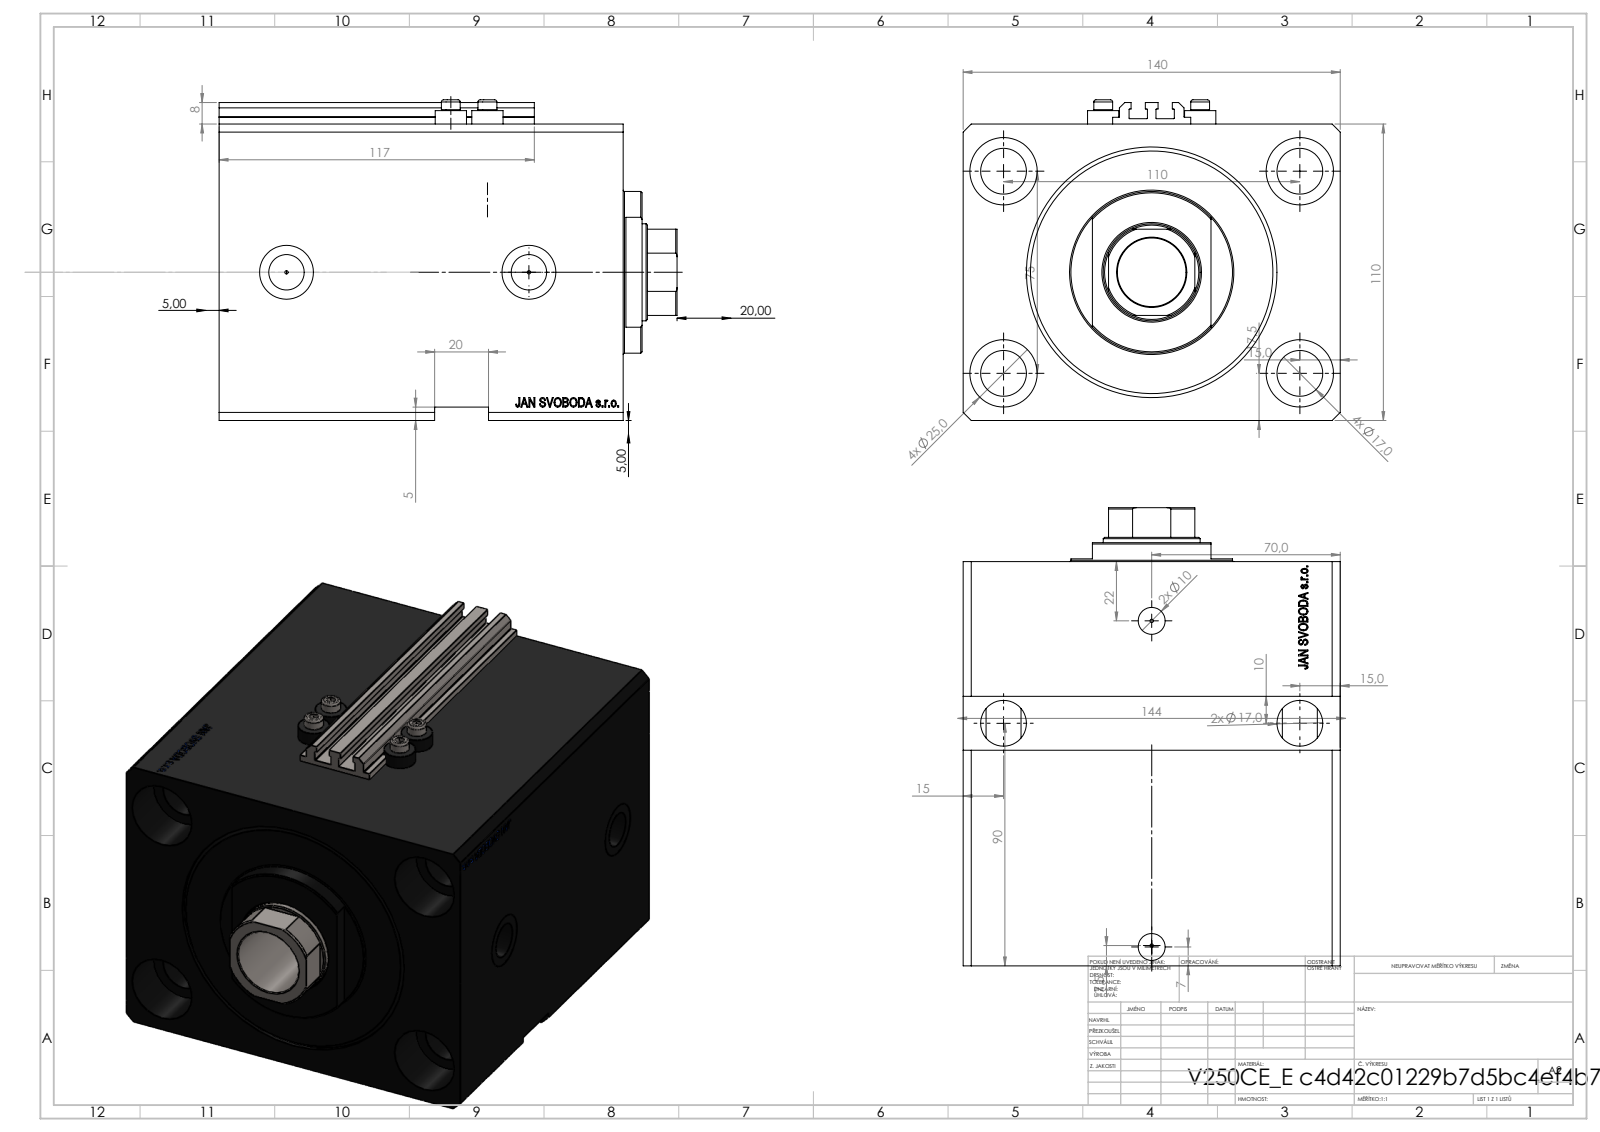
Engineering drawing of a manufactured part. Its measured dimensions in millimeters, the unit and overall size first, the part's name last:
Units: millimetres
Overall size (bounding box): 170 × 140 × 119
Round holes (diameter × count): ⌀17 ×8, ⌀1.25 ×4, ⌀4 ×4, ⌀25 ×4, ⌀10 ×2, ⌀13.16 ×2, ⌀20 ×2, ⌀25.5 ×1, ⌀36 ×1, ⌀80 ×1, ⌀93 ×1
Round bosses / shafts (diameter × count): ⌀11.6 ×4, ⌀7 ×4, ⌀60 ×1
Partial cylindrical surfaces — rounded edges, fillets, slot ends (radius × count): R0.2 ×10, R17.5 ×1
Main face-to-face distances: 110, 140, 150, 25, 125, 105, 20, 130, 50, 70
Hole centre spacings: 66.57, 110, 13.6, 30, 33.62, 36, 37.22, 38.23
Volume: 1 868 000 mm³ · Surface area: 259 858 mm²
Bodies: 8 solids, 1149 faces (553 planar, 158 cylindrical, 438 other)
Part name (STEP PRODUCT): V250CE_VC_E; V250CE_E_Body; V250CE_C_VCP; ALLEN BOLT V250CE
STEP written by: SolidWorks 2019 (CONFIG_CONTROL_DESIGN)
